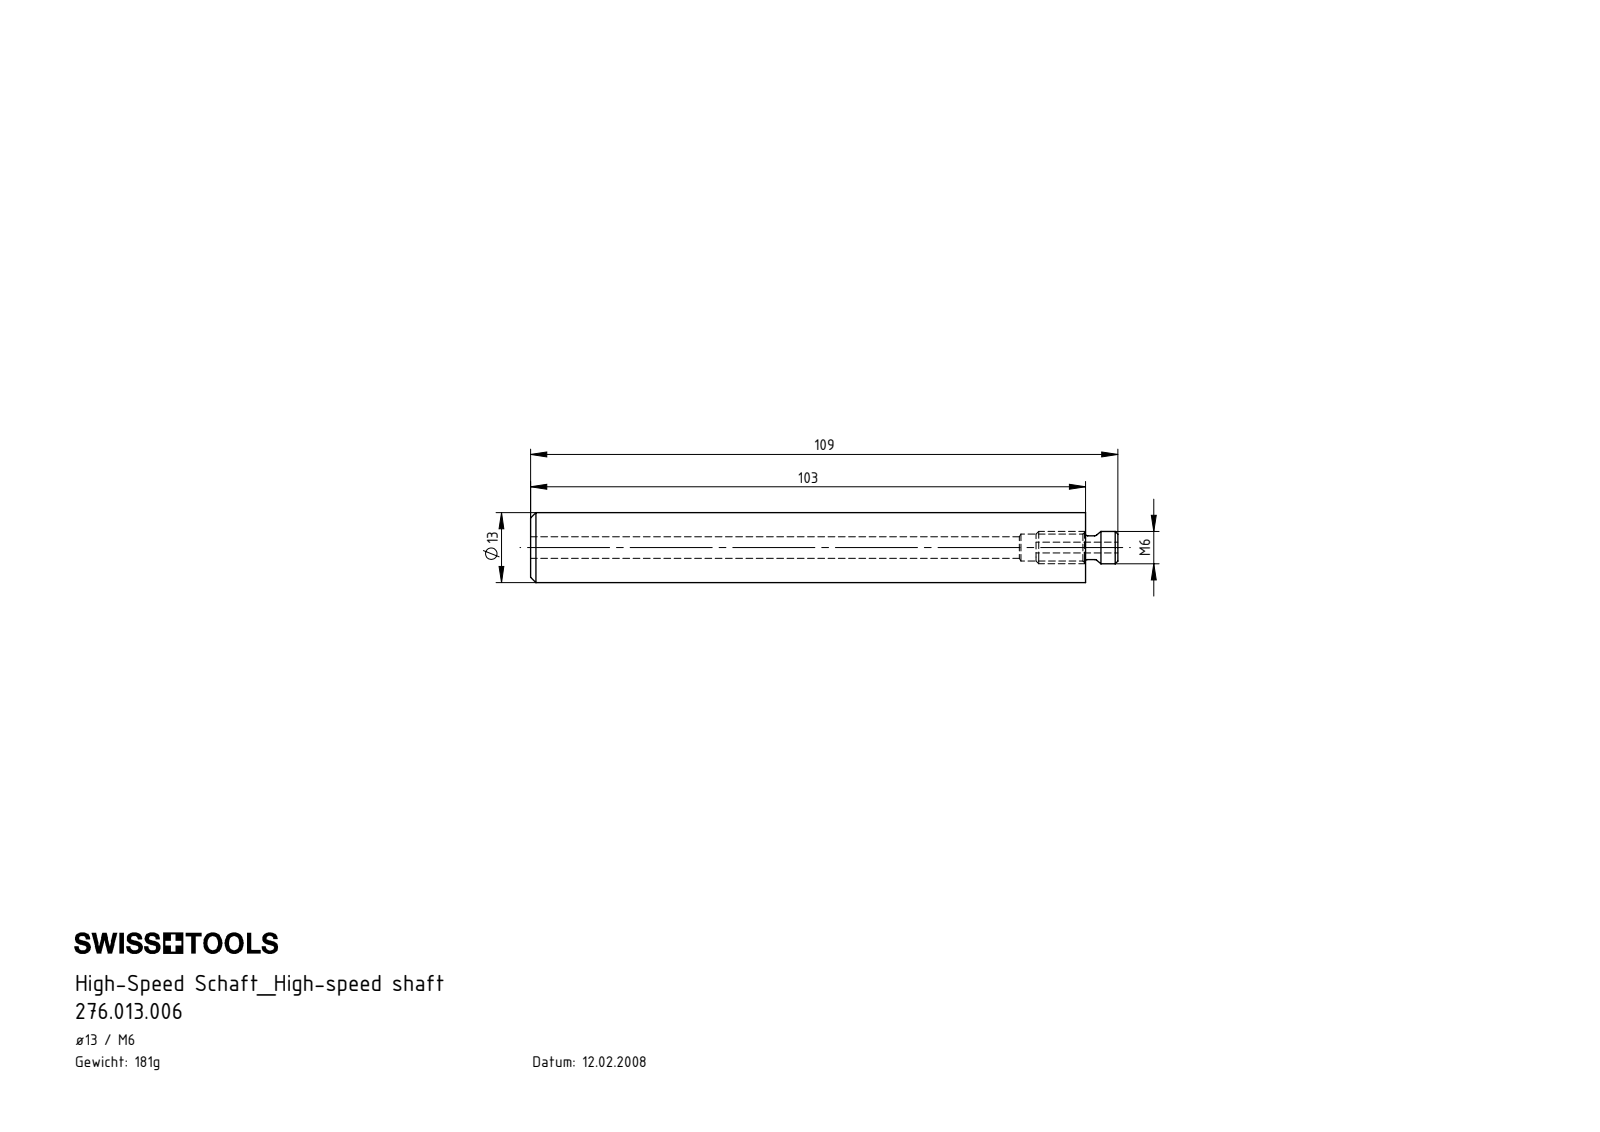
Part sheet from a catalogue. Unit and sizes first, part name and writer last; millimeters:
Units: millimetres
Overall size (bounding box): 109 × 13 × 13
Round holes (diameter × count): ⌀2 ×1, ⌀4 ×1, ⌀5 ×1
Round bosses / shafts (diameter × count): ⌀13 ×1, ⌀6 ×1, ⌀4.4 ×1
Main face-to-face distances: 103, 109, 6, 93.8, 9.2, 15.2, 102.8, 9, 6.2
Volume: 12 615 mm³ · Surface area: 6 169 mm²
Bodies: 2 solids, 35 faces (5 planar, 14 cylindrical, 16 other)
Part name (STEP PRODUCT): U13-HS6.K01.103_A; HM1-BG1.006.015_A; HM1-U13.001.103_A
STEP written by: SolidWorks 2017 (AUTOMOTIVE_DESIGN)
